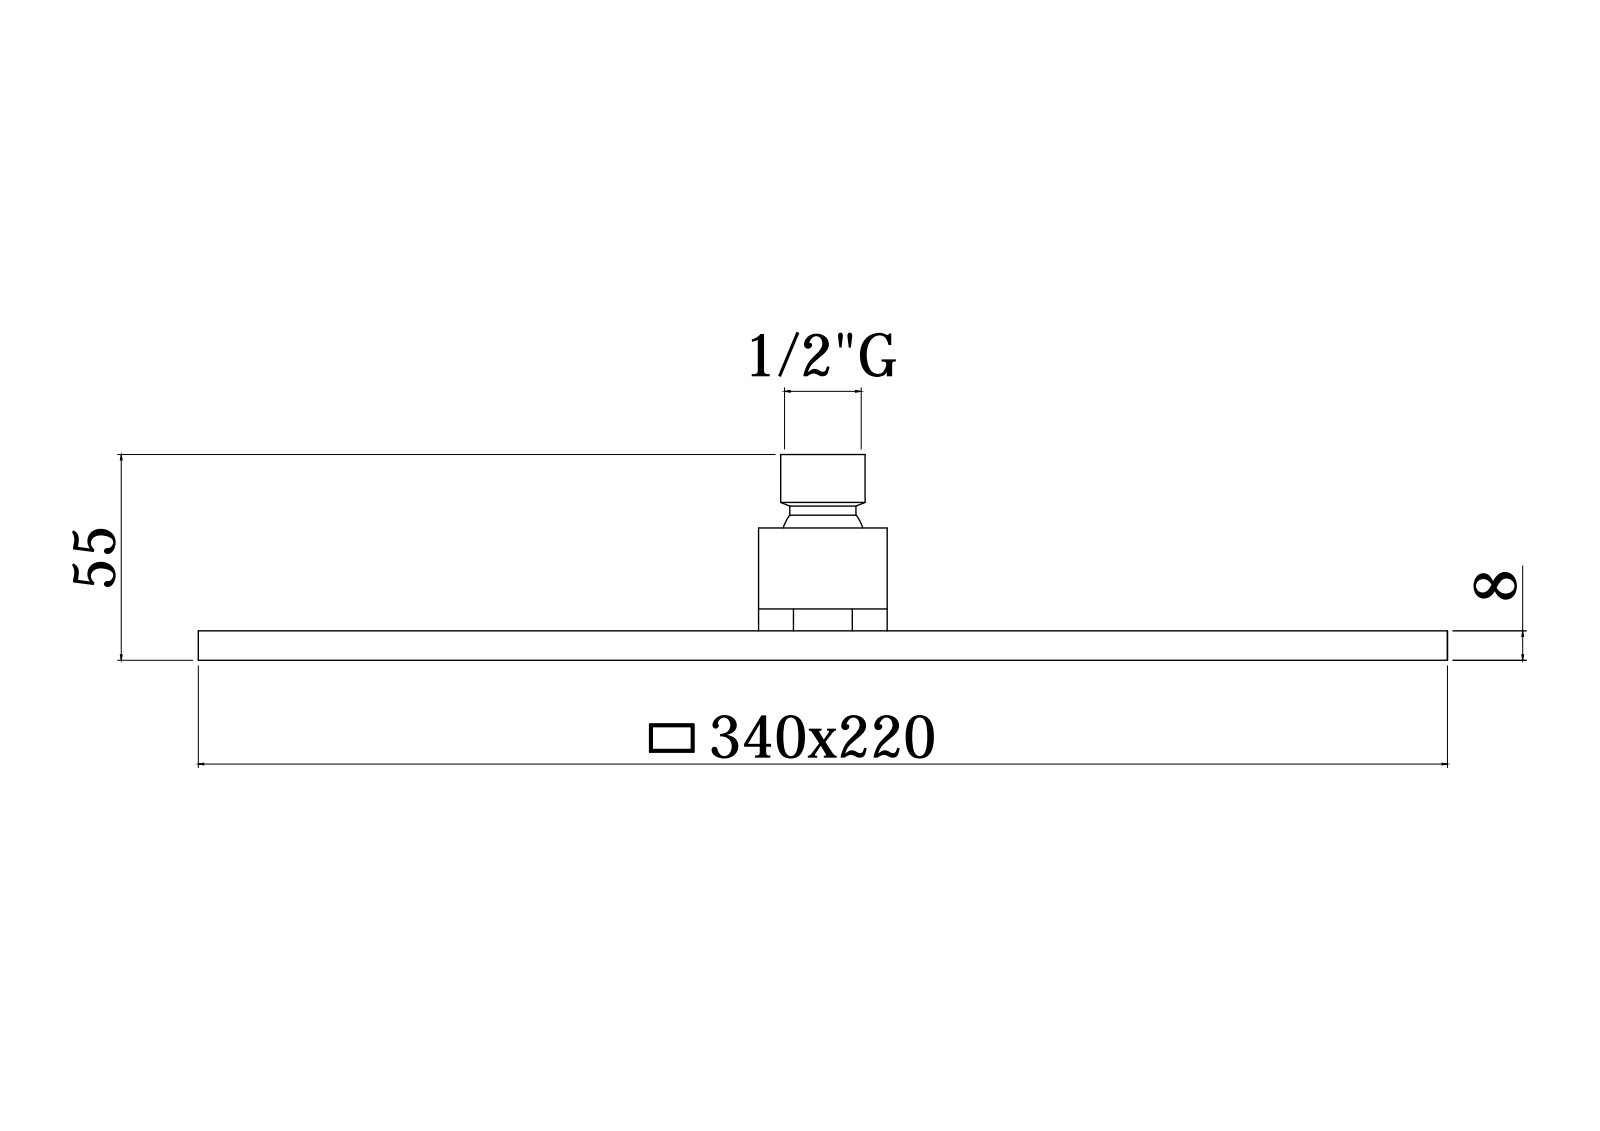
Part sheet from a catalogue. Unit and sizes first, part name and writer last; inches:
Units: inches
Overall size (bounding box): 13.386 × 8.661 × 2.043
Round holes (diameter × count): ⌀0.059 ×112, ⌀0.067 ×112, ⌀0.098 ×22, ⌀0.201 ×22, ⌀0.276 ×1, ⌀0.591 ×1, ⌀0.63 ×1, ⌀0.65 ×1, ⌀0.733 ×1, ⌀0.909 ×1, ⌀0.937 ×1, ⌀0.945 ×1
Round bosses / shafts (diameter × count): ⌀0.394 ×112, ⌀0.236 ×22, ⌀0.197 ×22, ⌀1.252 ×1, ⌀1.102 ×1, ⌀0.913 ×1, ⌀0.902 ×1
Partial cylindrical surfaces — rounded edges, fillets, slot ends (radius × count): R0.787 ×22, R0.039 ×4
Main face-to-face distances: 0.295, 0.039, 0.335, 0.059, 0.236, 0.276, 0.22, 0.114, 0.055, 0.181
Hole centre spacings: 1.89, 8.155, 3.78, 8.787, 5.669, 9.751, 7.933, 1.969
Volume: 14.82 in³ · Surface area: 512.5 in²
Bodies: 1 solid, 3979 faces (478 planar, 1012 cylindrical, 2489 other)
Part name (STEP PRODUCT): ZSOF091CR
STEP written by: CREO PARAMETRIC BY PTC INC, 2020044 (CONFIG_CONTROL_DESIGN)
